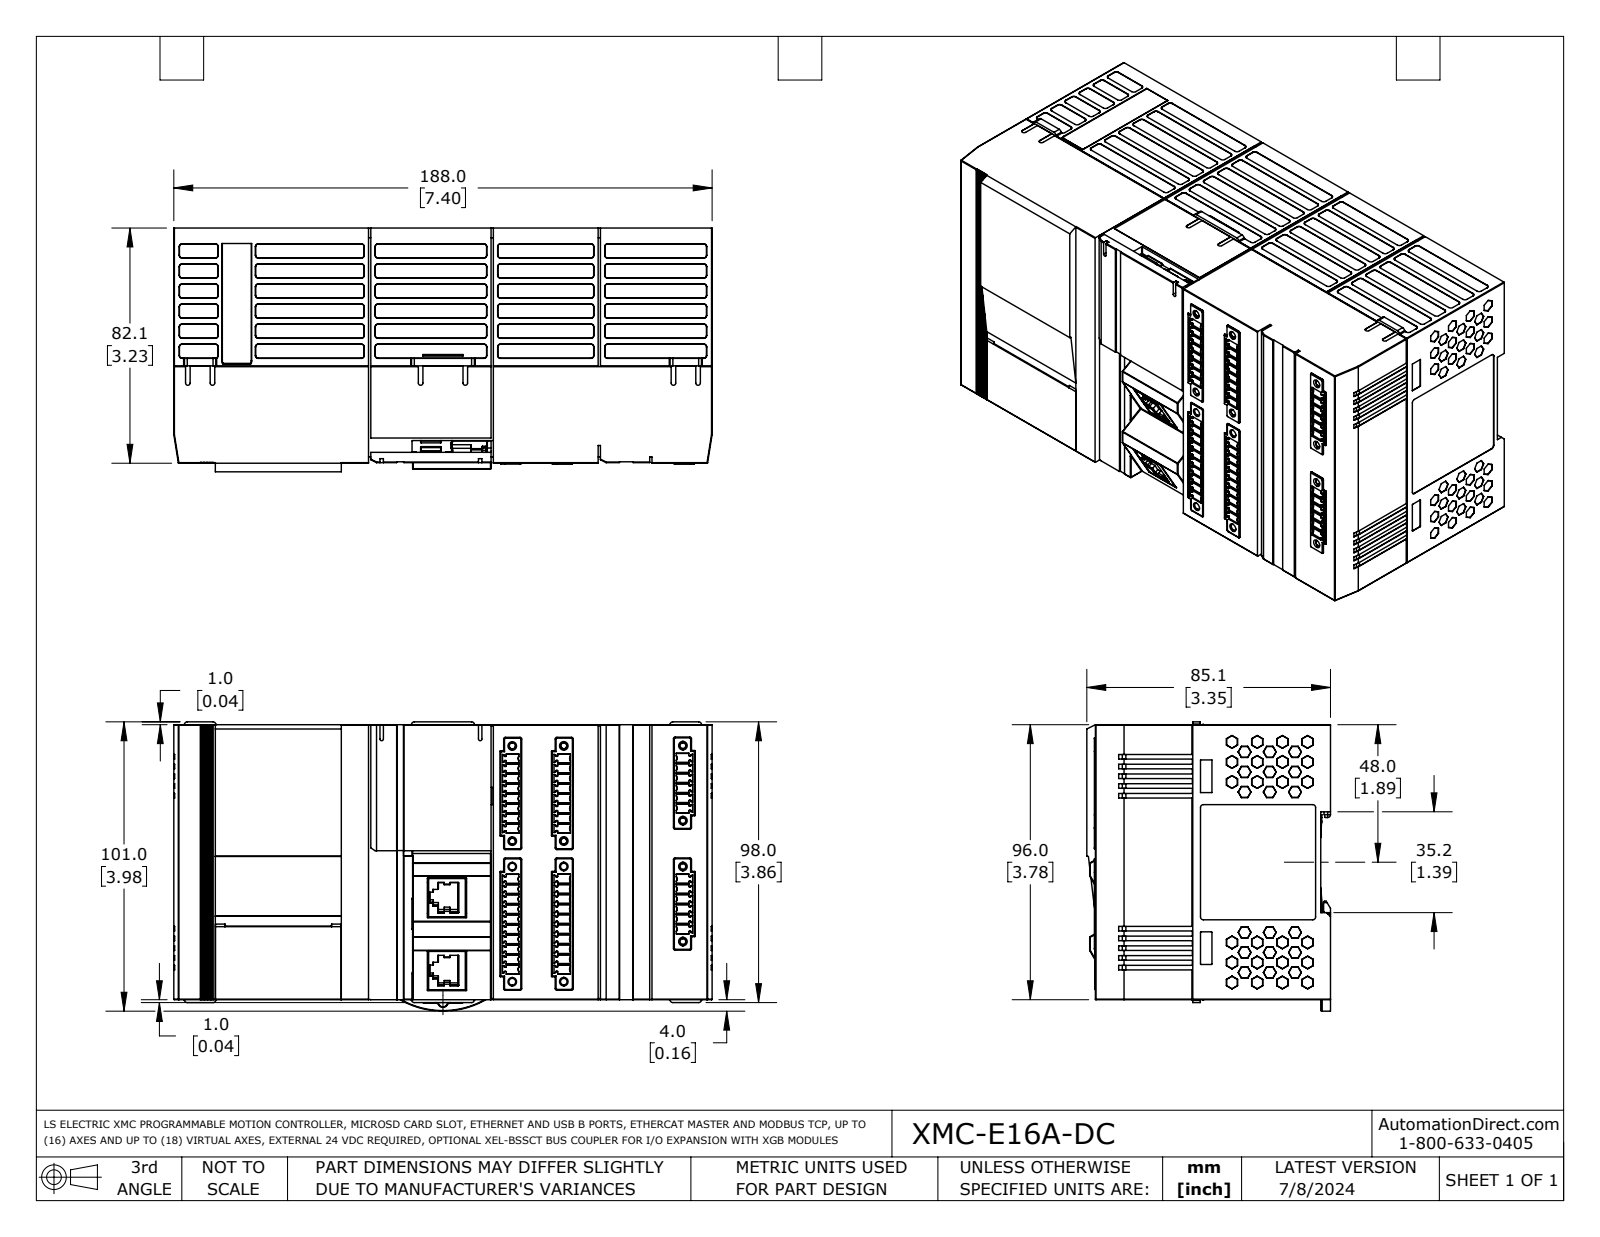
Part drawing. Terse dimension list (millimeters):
name: XMC-E16A-DC
written by: SolidWorks 2021 (AUTOMOTIVE_DESIGN)
unit: mm
bodies: 1 solid, 4897 faces (3156 planar, 1086 cylindrical, 655 other)
size: 188 × 101 × 85.1
volume: 1 427 000 mm³; area: 101 200 mm²
holes: 4× ⌀2, 1× ⌀2.1, 1× ⌀2.5, 1× ⌀3.4
bosses: 5× ⌀5.3, 5× ⌀3, 4× ⌀2, 1× ⌀5.2, 1× ⌀4
rounds: 448× R0.2, 144× R0.5, 87× R1, 46× R0.3, 40× R1.6, 27× R0.6, 12× R0.3, 7× R0.8
face distances: 95.9, 96, 78.7, 95.9, 187.9, 82.1, 188, 3.4, 78.5, 81.9
hole spacings: 11.8, 16, 26.2, 26.2, 28.1, 42.2, 42.2, 43.2
